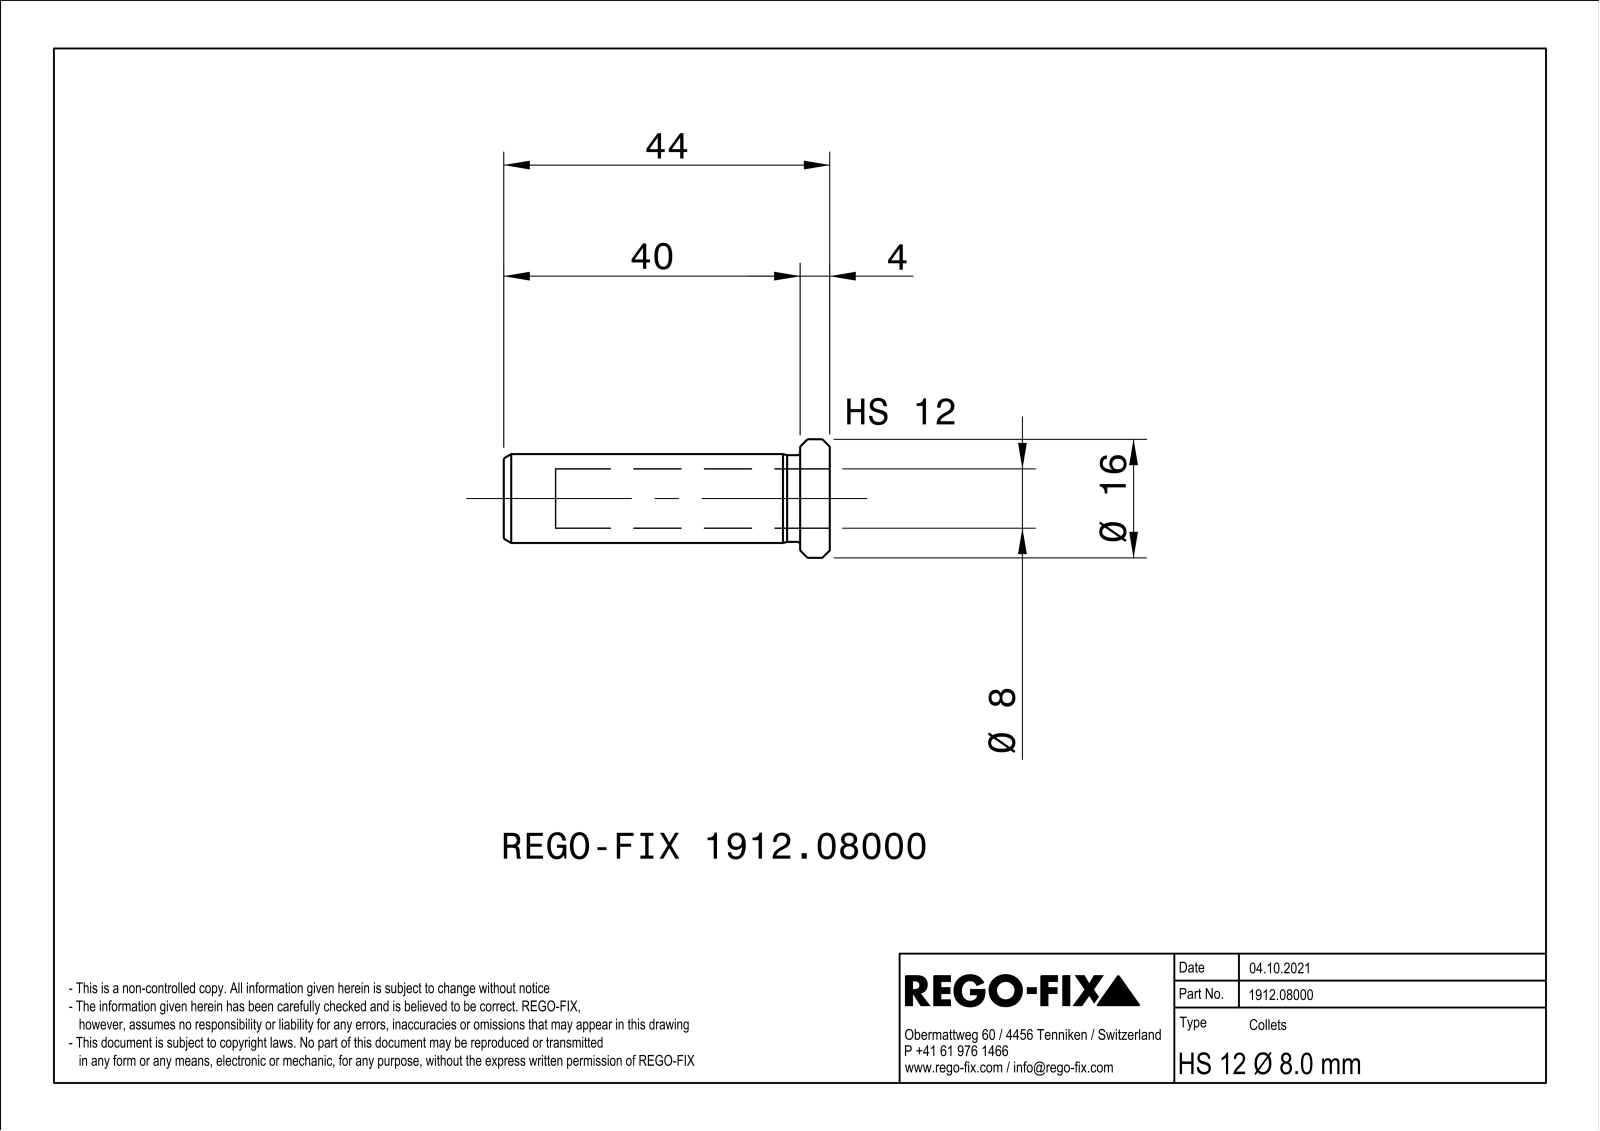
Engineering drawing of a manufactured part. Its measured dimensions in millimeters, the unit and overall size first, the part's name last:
Units: millimetres
Overall size (bounding box): 44 × 15.98 × 15.98
Round holes (diameter × count): ⌀8 ×1, ⌀8.2 ×1
Round bosses / shafts (diameter × count): ⌀16 ×1, ⌀12 ×1, ⌀11.7 ×1
Main face-to-face distances: 0.8, 44, 4, 40
Volume: 2 796 mm³ · Surface area: 3 396 mm²
Bodies: 1 solid, 71 faces (22 planar, 11 cylindrical, 38 other)
Part name (STEP PRODUCT): NOCUT
STEP written by: SIEMENS PLM Software Solid Edge ST10 (AUTOMOTIVE_DESIGN)
